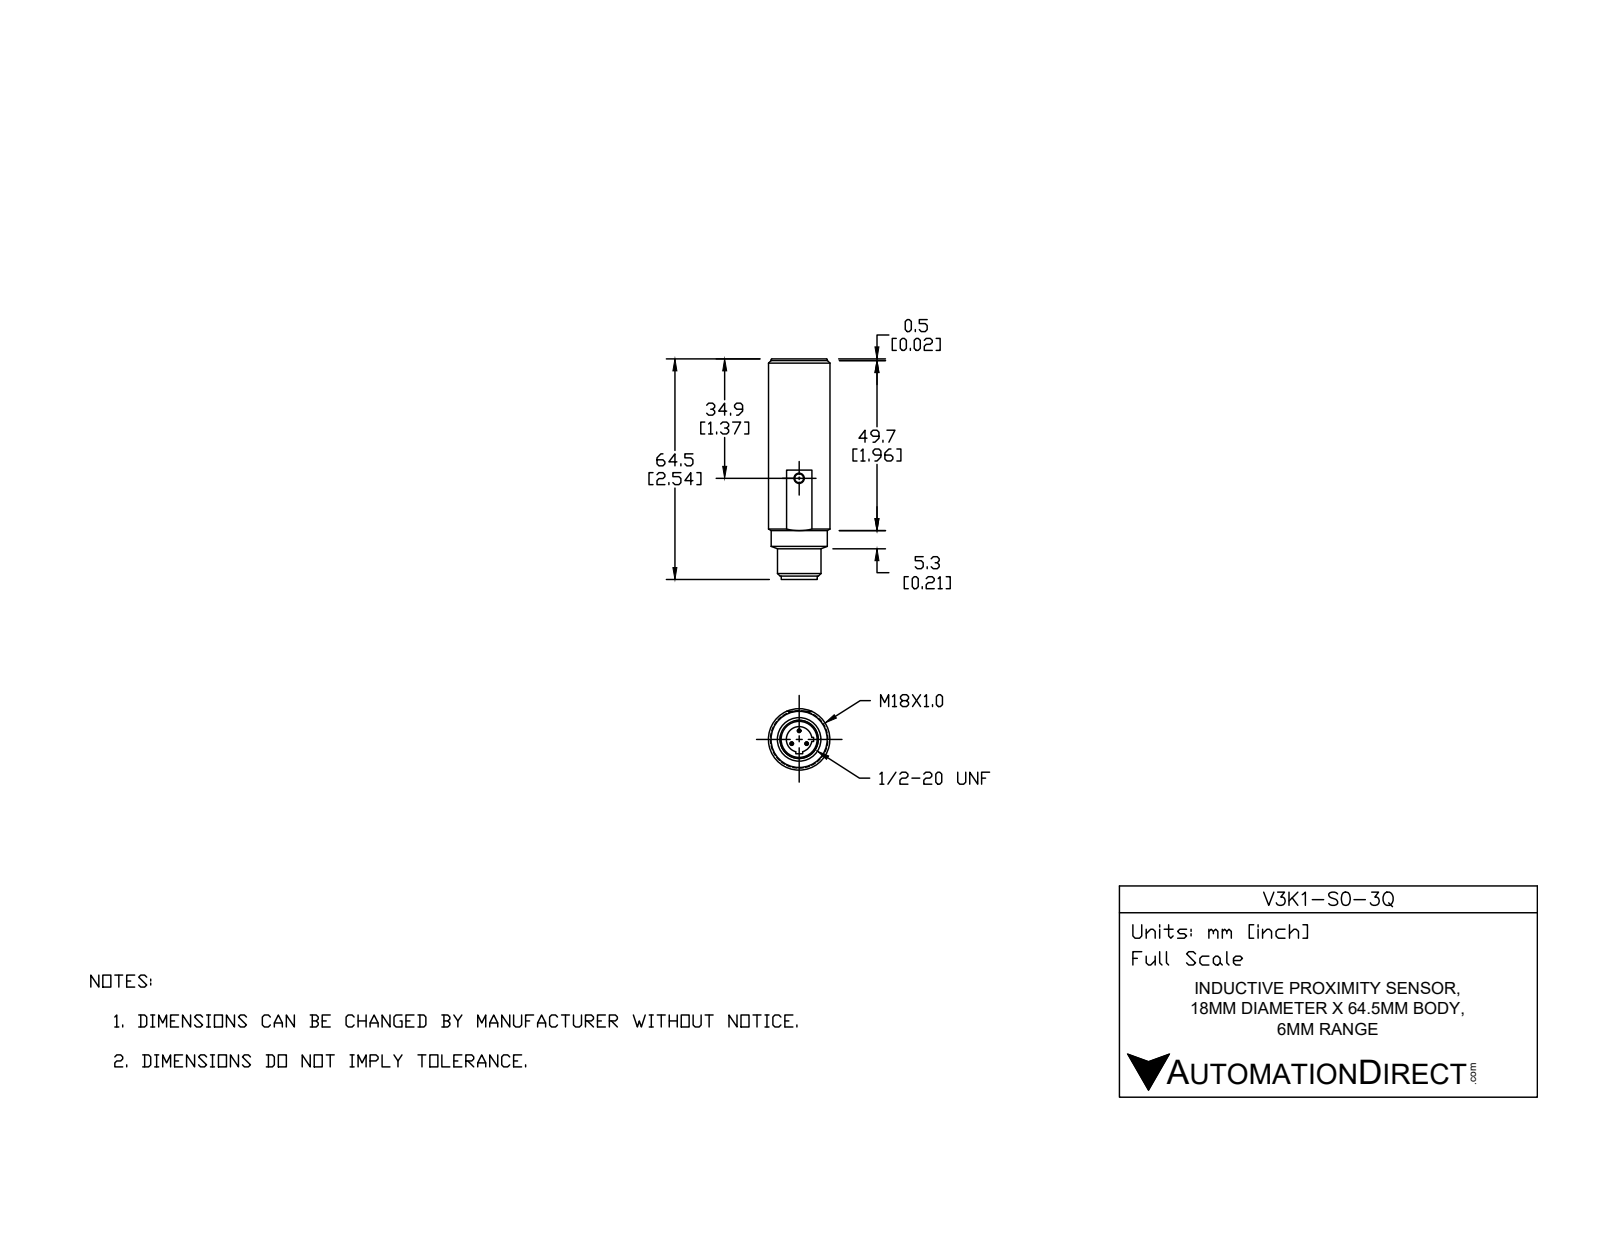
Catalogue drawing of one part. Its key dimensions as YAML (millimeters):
part_name: "V3K1_3Q_fig"
step_written_by: "ST-DEVELOPER v16.7 (AUTOMOTIVE_DESIGN)"
units: millimeters
bodies: {solids: 3, faces: 53, planar: 26, cylindrical: 17, other: 10}
overall_size: [64.5, 18, 18]
volume: 14510
surface_area: 4368
round_holes:
  - {diameter: 1, count: 3}
  - {diameter: 2.6, count: 1}
  - {diameter: 7.5, count: 1}
  - {diameter: 9.5, count: 1}
round_bosses_or_shafts:
  - {diameter: 0.98, count: 3}
  - {diameter: 18, count: 1}
  - {diameter: 16.4, count: 1}
  - {diameter: 12.7, count: 1}
  - {diameter: 10.5, count: 1}
  - {diameter: 9.55, count: 1}
  - {diameter: 9.4, count: 1}
face_to_face_distances: [57.4, 64.5, 7.1, 1, 63.5, 6.1, 12.4, 1.2, 7.6, 6.4]
hole_center_spacings: [2.5, 4.33, 4.34]
